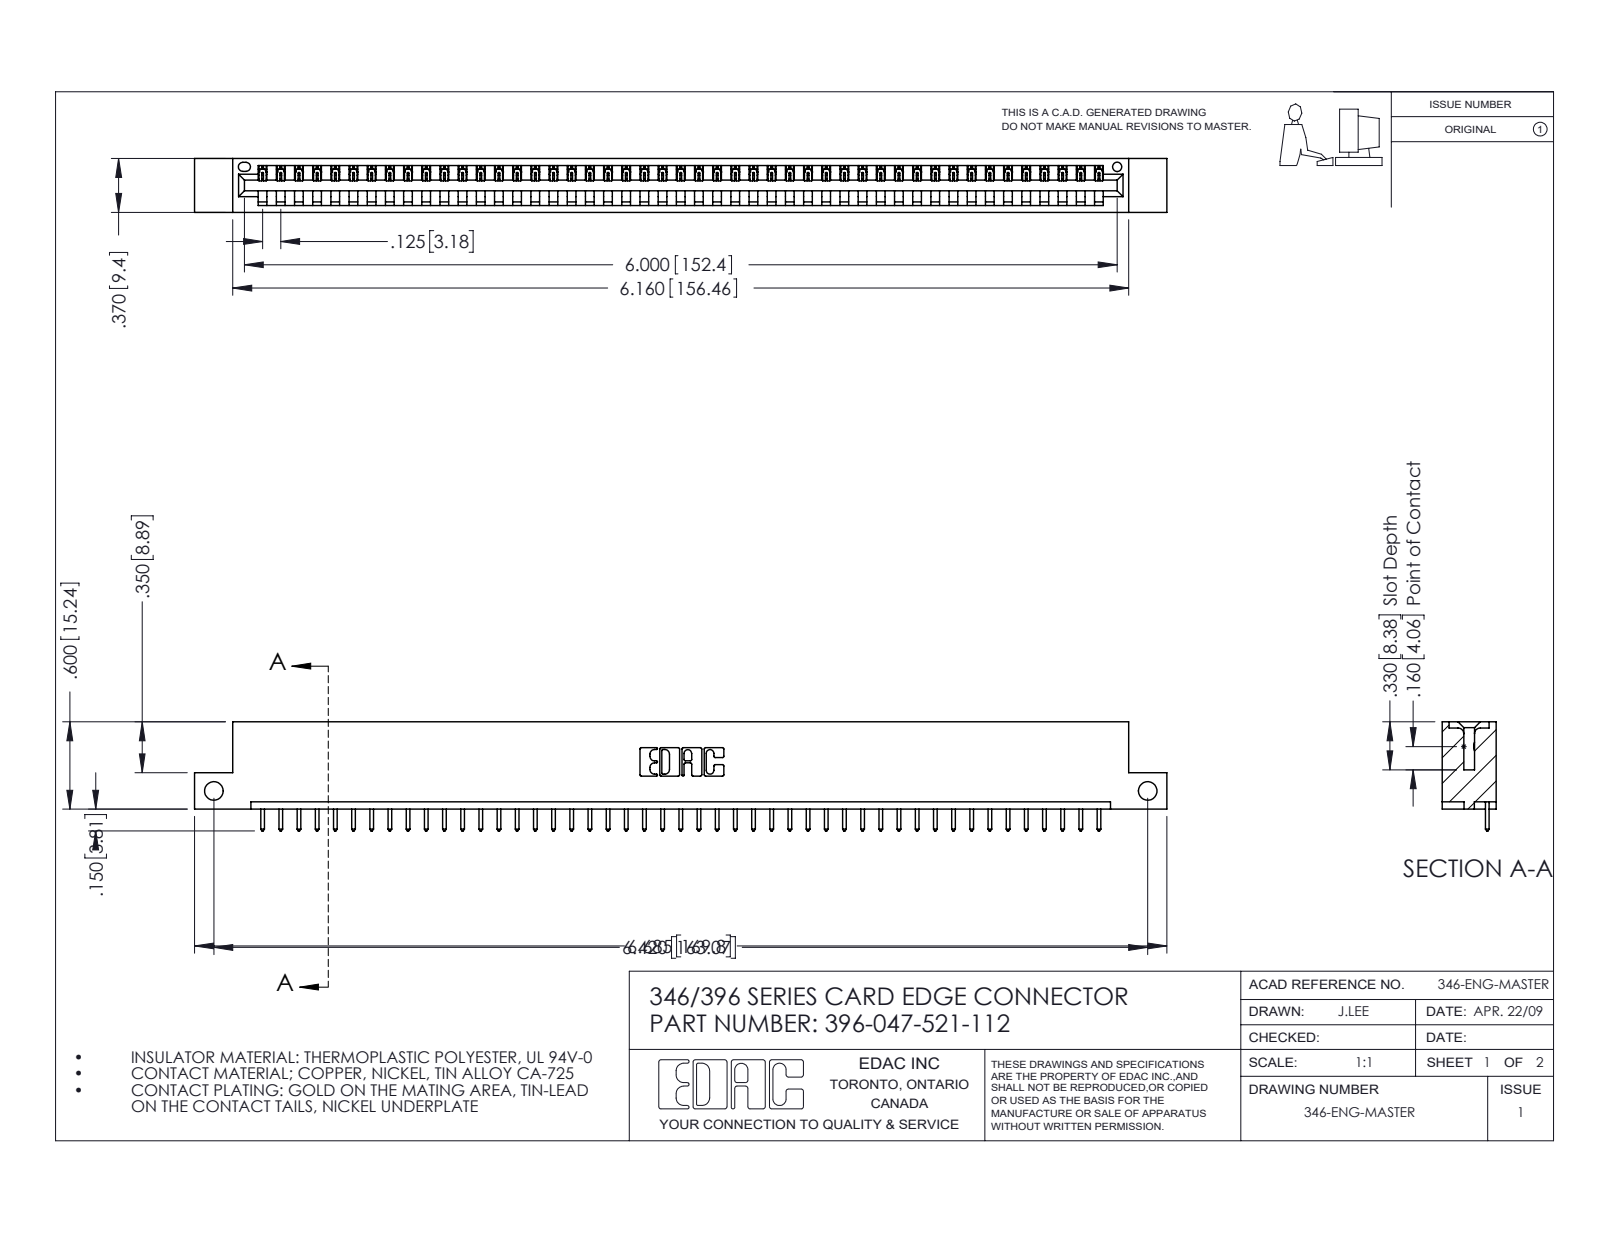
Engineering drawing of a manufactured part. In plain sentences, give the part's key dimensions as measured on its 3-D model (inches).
The part is named "396-047-521-112; 346 Part_Flush Mounting Lugs - Side Mount; 345-292-001_345-293-121". Its 3-D file was written by "SolidWorks 2016 (CONFIG_CONTROL_DESIGN)". It is 48 solids with 2848 faces: 1956 planar, 892 cylindrical and 0 other. Overall it measures 6.685 by 0.75 by 0.37 inches. Its volume is 0.98 cubic inches and its surface area 30.16 square inches. Round holes: 2 of diameter 0.128, 1 of diameter 0.064. Partial cylindrical surfaces (rounded edges, fillets, slot ends): 94 of radius 0.006, 94 of radius 0.01, 22 of radius 0.01, 6 of radius 0.007, 6 of radius 0.031, 3 of radius 0.026, 2 of radius 0.031, 2 of radius 0.04. The main face-to-face distances are 0.048, 0.322, 0.37, 0.25, 0.072, 0.298, 0.025, 0.148, 0.222, 0.1. The hole center spacings are 6.42.
